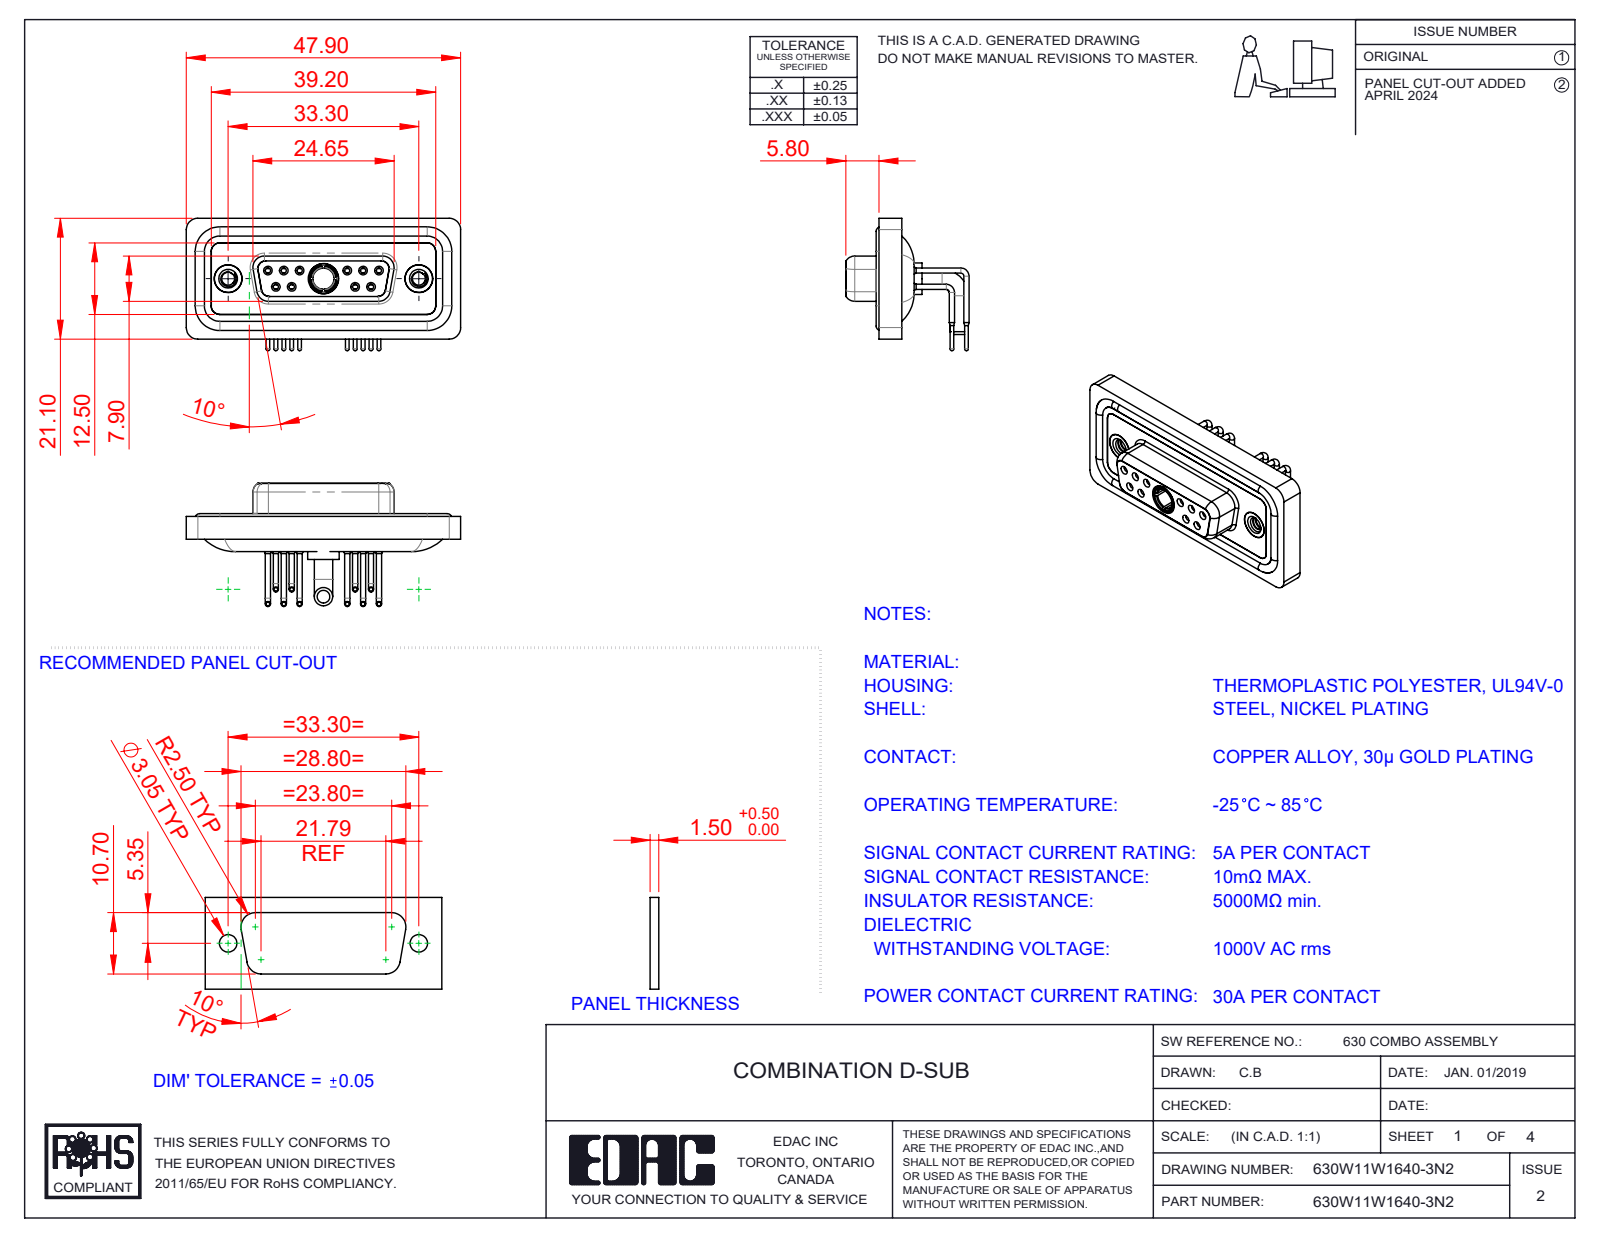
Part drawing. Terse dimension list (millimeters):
name: 630Combo Shell Front_15 Contacts; Power Socket_30A RA; 630W11W1640-3N2; 630Combo Threaded Rivet_2 (+5 more)
written by: SolidWorks 2023 (CONFIG_CONTROL_DESIGN)
unit: mm
bodies: 19 solids, 994 faces (284 planar, 443 cylindrical, 267 other)
size: 47.9 × 23.12 × 21.53
volume: 6 246 mm³; area: 10 489 mm²
holes: 10× ⌀0.9, 10× ⌀1.1, 10× ⌀1.5, 10× ⌀2, 6× ⌀1.7, 4× ⌀1.6, 3× ⌀4.85, 2× ⌀2.26, 2× ⌀4, 2× ⌀4.05, 2× ⌀5, 1× ⌀3.7
bosses: 10× ⌀1.6, 10× ⌀0.9, 10× ⌀0.65, 2× ⌀4.95, 2× ⌀4.8, 2× ⌀3.2, 1× ⌀5.5, 1× ⌀5.2
rounds: 20× R2, 18× R1.5, 12× R1.35, 8× R1.6, 4× R0.25, 4× R0.5, 4× R0.6, 4× R0.65
face distances: 0.4, 1.8, 1.1, 1.6, 2.5, 2.9, 3.1, 3.7, 4.1, 1.5
hole spacings: 3.16, 2.77, 13.85, 11.08, 16.62, 5.03, 5.04, 5.54
